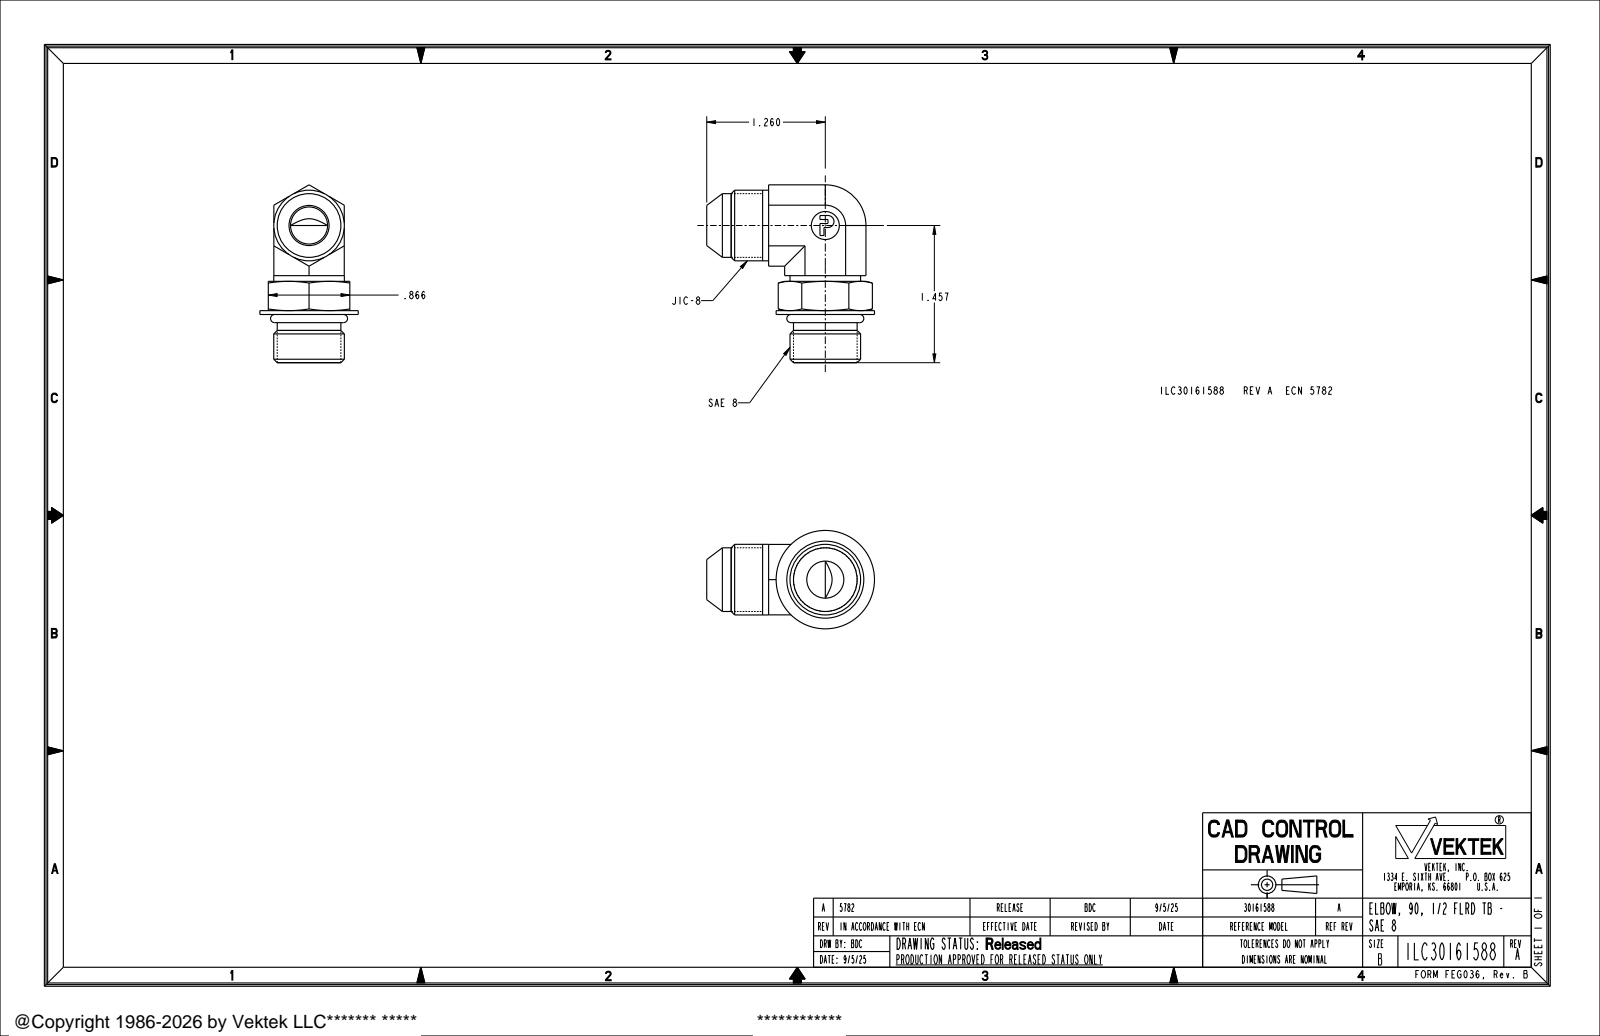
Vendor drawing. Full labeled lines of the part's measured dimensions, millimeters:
Part name (STEP PRODUCT): ILC30161588
STEP written by: CREO PARAMETRIC BY PTC INC, 2021164 (AUTOMOTIVE_DESIGN)
Units: millimetres
Bodies: 1 solid, 159 faces (82 planar, 45 cylindrical, 32 other)
Overall size (bounding box): 48 × 45.3 × 26.5
Volume: 15 400 mm³ · Surface area: 10 150 mm²
Round holes (diameter × count): ⌀10 ×2, ⌀7.6 ×1, ⌀17.9 ×1
Round bosses / shafts (diameter × count): ⌀19.1 ×2, ⌀17.2 ×2, ⌀26.5 ×1
Partial cylindrical surfaces — rounded edges, fillets, slot ends (radius × count): R0.8 ×4, R0.5 ×2, R10.6 ×2, R11.4 ×2, R12 ×2, R1.6 ×1
Main face-to-face distances: 19, 1.5, 20.5, 22, 13, 0.4, 0.6, 8.7, 4.3, 13.6
